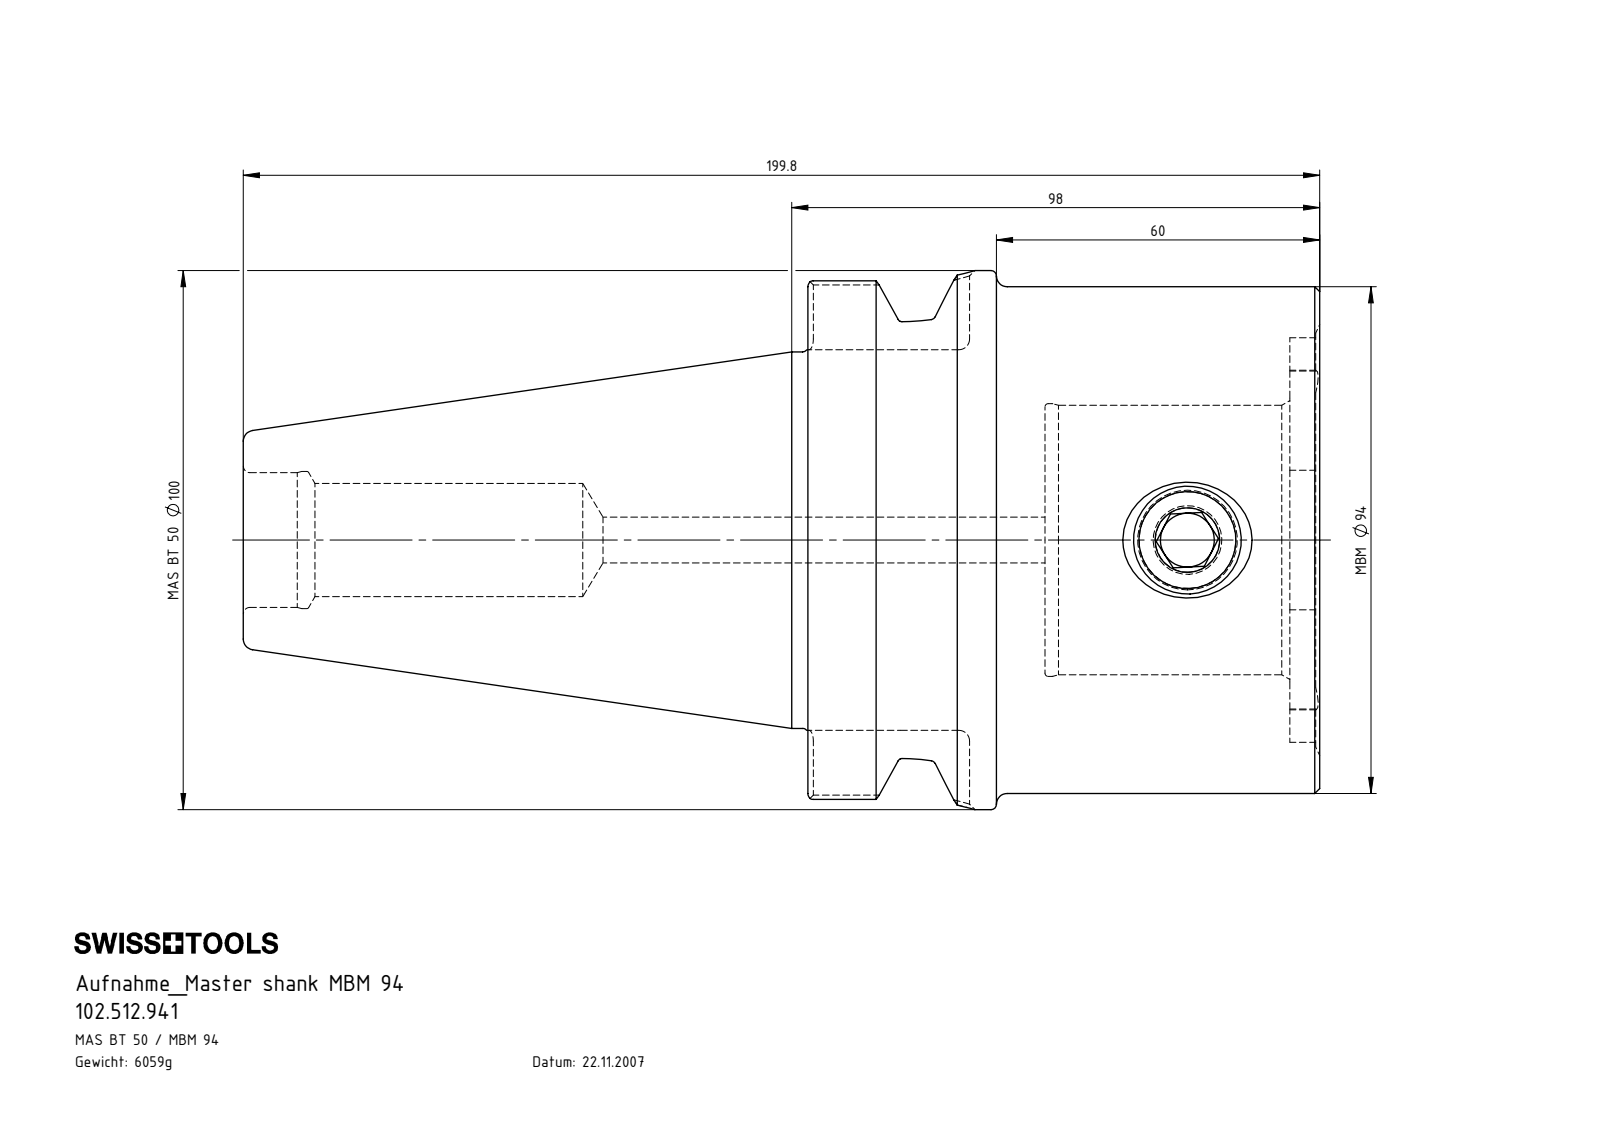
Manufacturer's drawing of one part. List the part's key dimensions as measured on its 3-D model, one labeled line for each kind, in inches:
Part name (STEP PRODUCT): BT5.MB9.K01.098; MB9-ER1.001.032_A; BT5-MB9.K01.098_C
STEP written by: SolidWorks 2017 (AUTOMOTIVE_DESIGN)
Units: inches
Bodies: 2 solids, 114 faces (42 planar, 34 cylindrical, 38 other)
Overall size (bounding box): 7.866 × 3.937 × 3.937
Volume: 47.1 in³ · Surface area: 123.5 in²
Round holes (diameter × count): ⌀0.335 ×1, ⌀0.394 ×1, ⌀0.728 ×1, ⌀0.827 ×1, ⌀0.984 ×1, ⌀1.002 ×1, ⌀1.969 ×1, ⌀1.992 ×1
Round bosses / shafts (diameter × count): ⌀3.937 ×1, ⌀3.701 ×1, ⌀3.346 ×1, ⌀2.75 ×1, ⌀0.787 ×1
Partial cylindrical surfaces — rounded edges, fillets, slot ends (radius × count): R0.079 ×8, R0.205 ×4, R0.506 ×1, R1.181 ×1, R1.477 ×1
Main face-to-face distances: 1.732, 3.522, 1.789, 3.74, 2.008, 0.219, 3.711, 1.978, 0.189, 0.03
